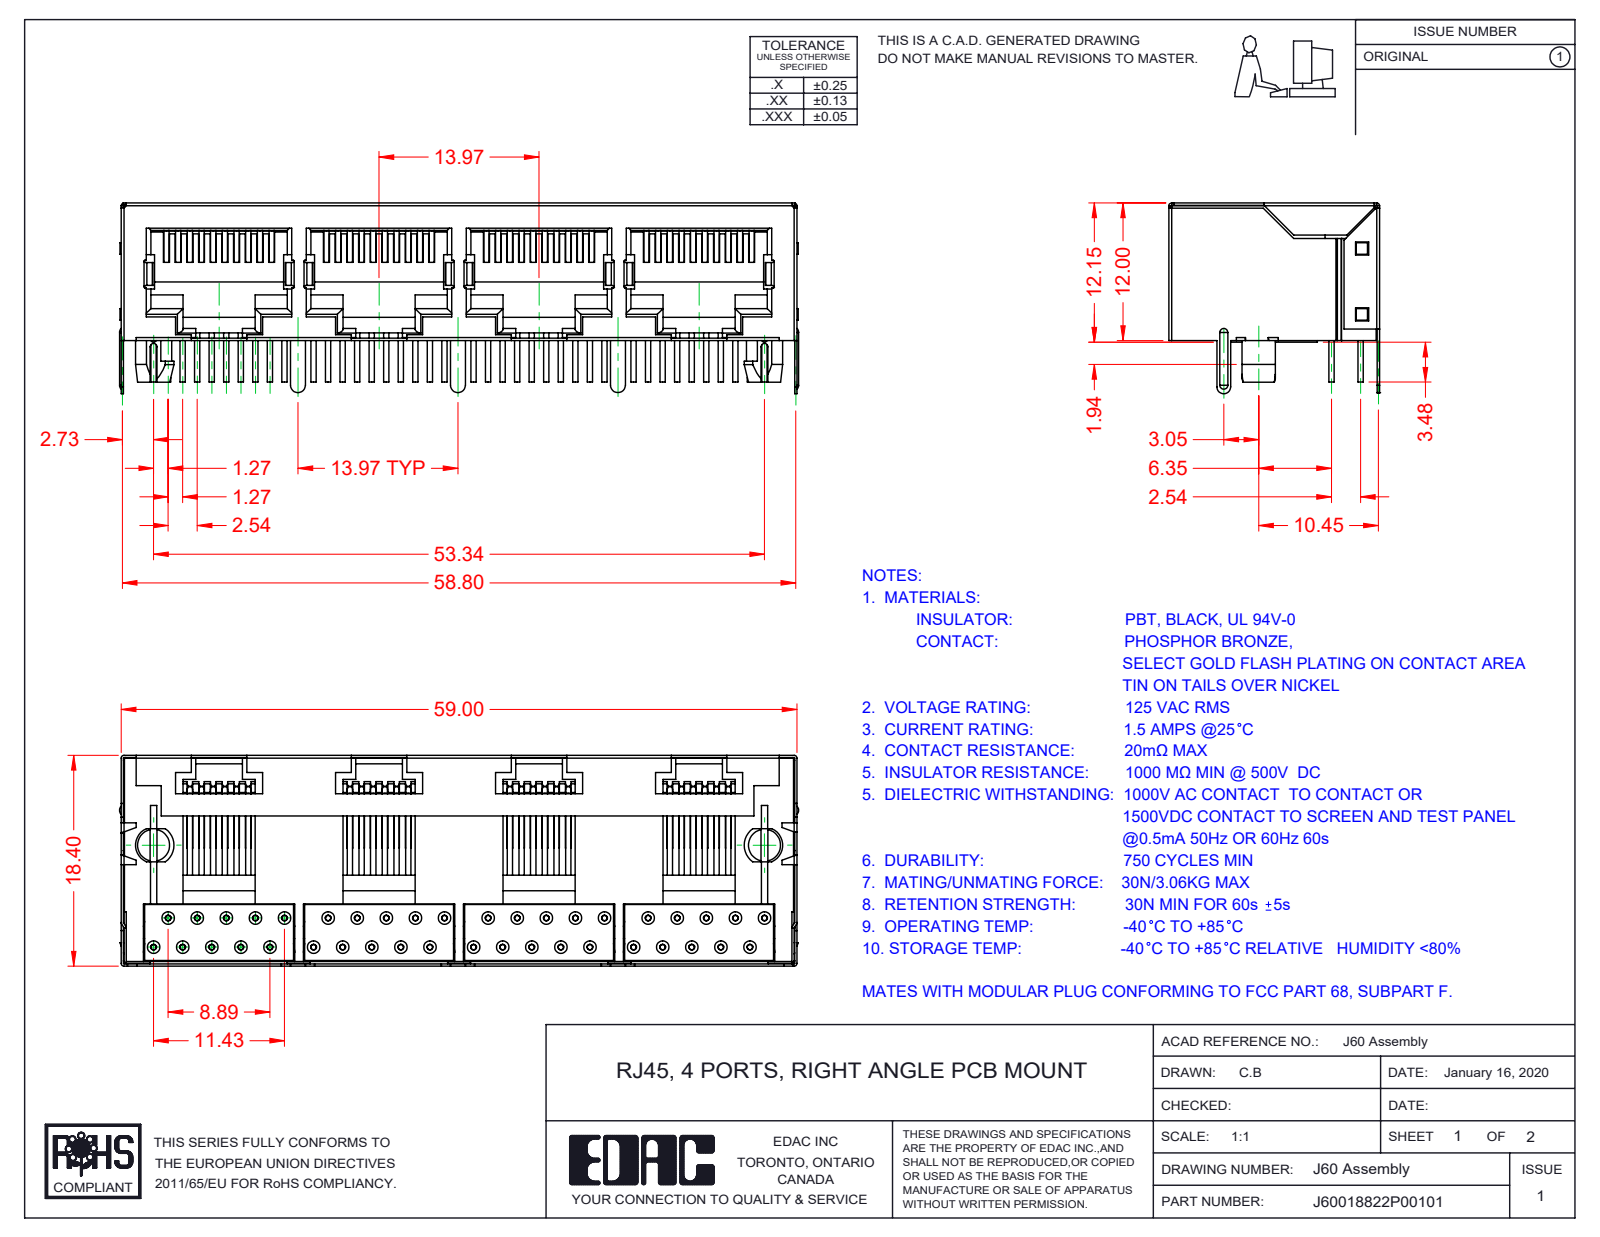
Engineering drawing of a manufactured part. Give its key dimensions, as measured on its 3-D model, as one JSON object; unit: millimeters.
{"part_name": "60 Insulator; RJ60041122P00101; 60 Contacts_10P10C; 60 Shield", "step_written_by": "SolidWorks 2016 (CONFIG_CONTROL_DESIGN)", "units": "millimeters", "bodies": {"solids": 42, "faces": 2674, "planar": 1505, "cylindrical": 763, "other": 406}, "overall_size": [59.3, 18.4, 16.65], "volume_mm3": 7062, "surface_area_mm2": 18987, "round_holes": [[0.5, 40], [1.1, 40]], "round_bosses_or_shafts": [[0.46, 120]], "partial_cylinders_radius": [[0.3, 26], [0.25, 21], [0.5, 18], [0.1, 16], [0.21, 10], [0.8, 7], [0.65, 3], [0.28, 2]], "face_to_face_distances": [0.5, 11.75, 11.55, 13.97, 2.19, 5.38, 5.18, 4.88, 18.2, 11.5], "hole_center_spacings": [2.84, 2.54, 4.58, 13.97, 5.08, 12.95, 15.45, 11.43]}
